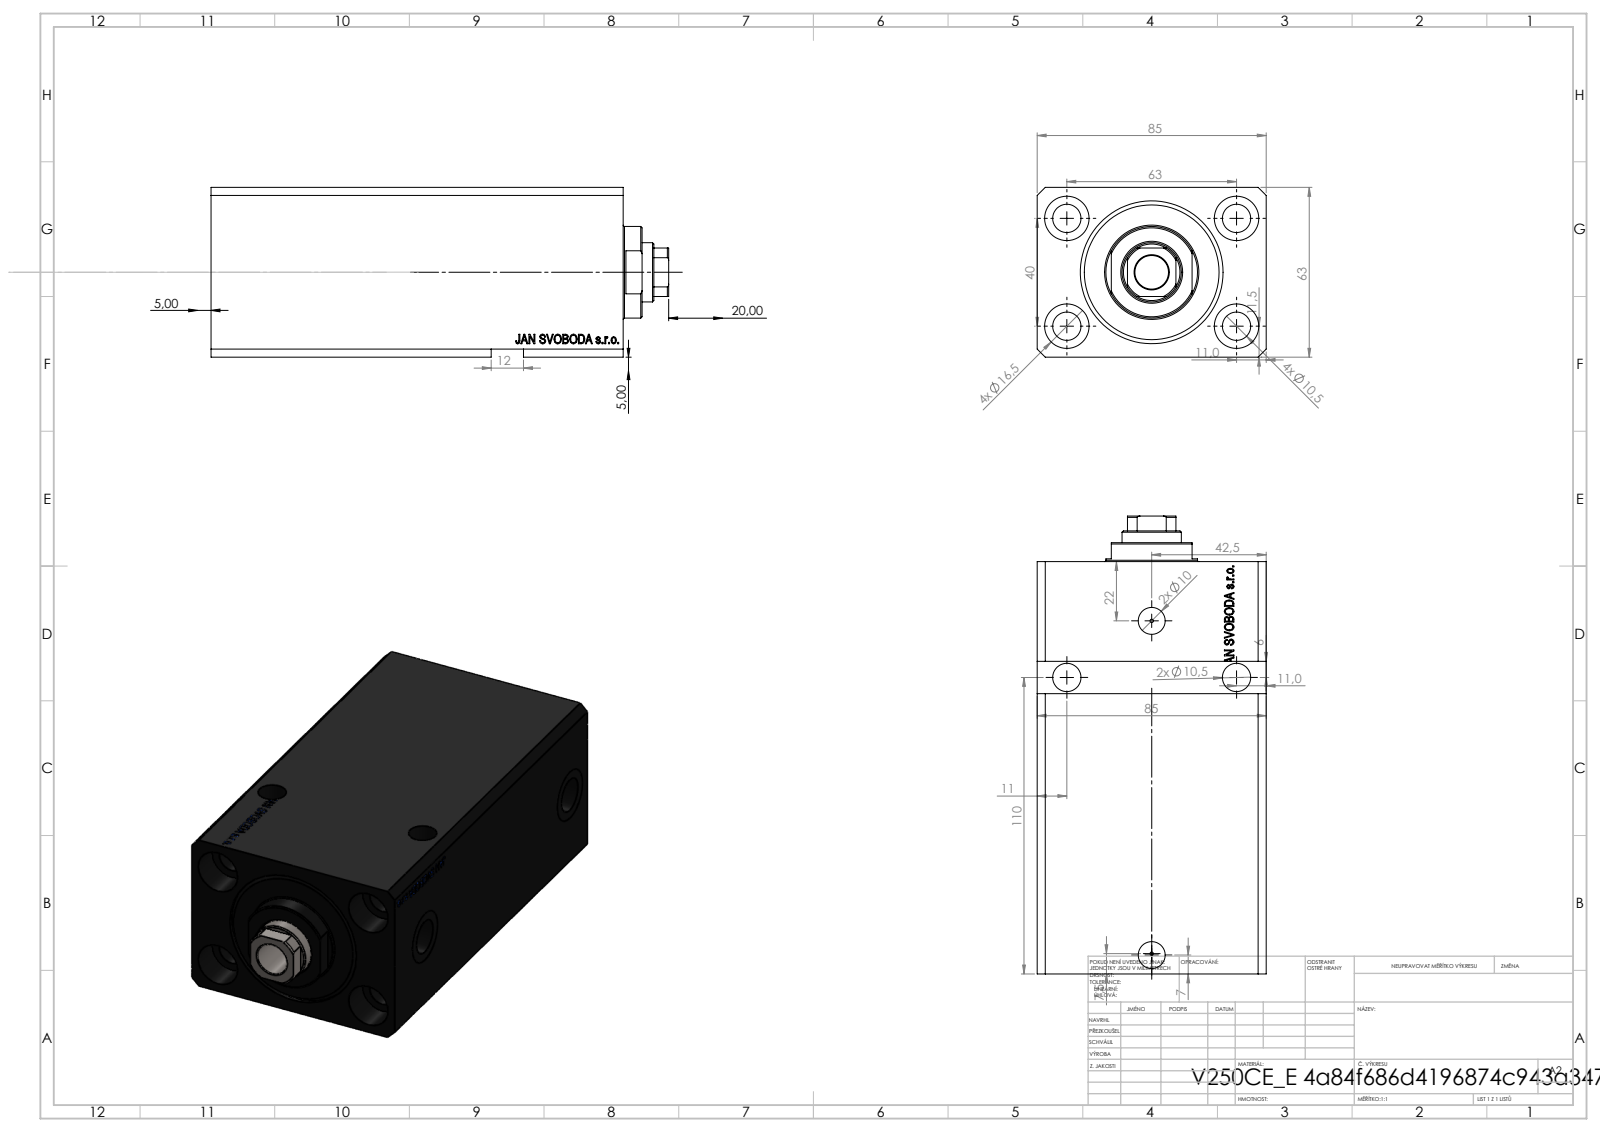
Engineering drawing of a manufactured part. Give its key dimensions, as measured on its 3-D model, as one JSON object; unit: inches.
{"part_name": "V250CE_E_Body; V250CE_C_VCP; V250CE_VC_E", "step_written_by": "SolidWorks 2019 (CONFIG_CONTROL_DESIGN)", "units": "inches", "bodies": {"solids": 3, "faces": 937, "planar": 459, "cylindrical": 104, "other": 374}, "overall_size": [6.693, 3.346, 2.48], "volume_in3": 40.65, "surface_area_in2": 195.7, "round_holes": [[0.413, 8], [0.049, 4], [0.65, 4], [0.394, 2], [0.518, 2], [0.787, 2], [0.492, 1], [0.866, 1], [1.575, 1], [2.087, 1]], "round_bosses_or_shafts": [[1.339, 1]], "partial_cylinders_radius": [[0.413, 1]], "face_to_face_distances": [2.48, 3.346, 6.024, 0.669, 5.354, 0.449, 4.906, 5.575, 2.205, 2.362], "hole_center_spacings": [1.469, 2.48, 1.491, 1.575, 1.646, 1.659, 2.938, 2.953]}
